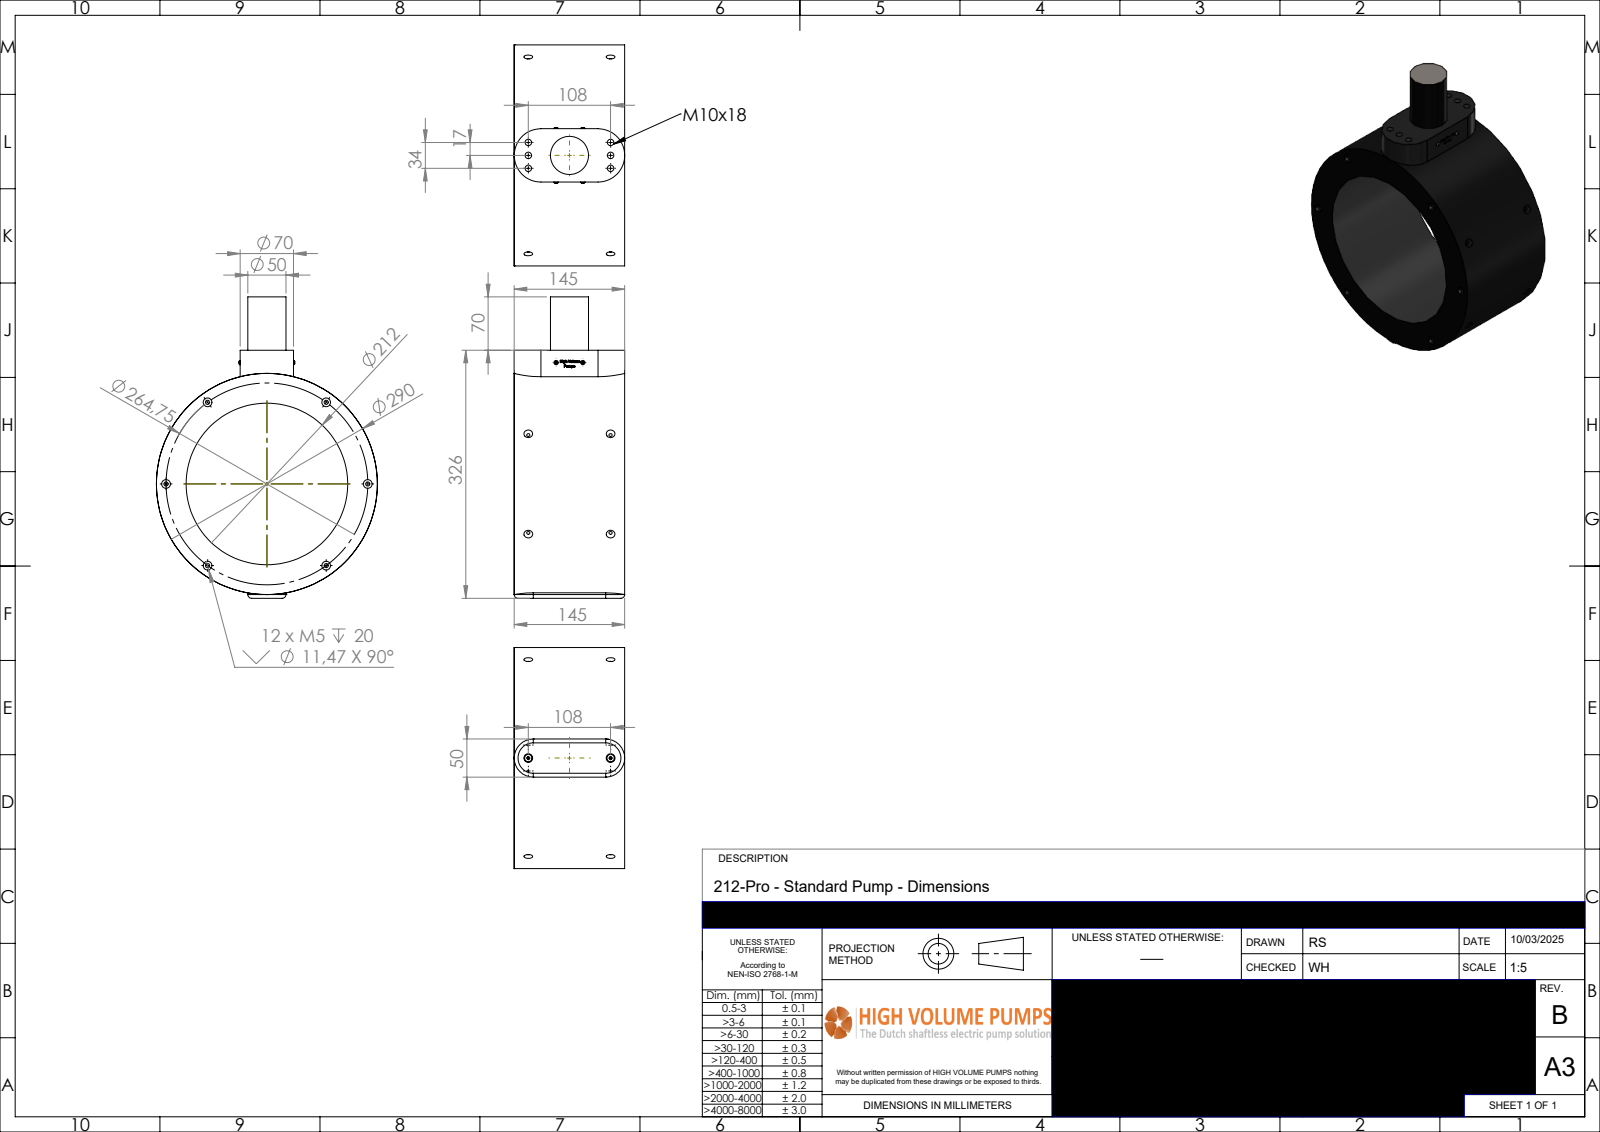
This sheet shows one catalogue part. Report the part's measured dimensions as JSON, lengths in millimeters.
{"part_name": "P-212-530-rev-B-SP", "step_written_by": "SolidWorks 2024 (AUTOMOTIVE_DESIGN)", "units": "millimeters", "bodies": {"solids": 1, "faces": 639, "planar": 337, "cylindrical": 45, "other": 257}, "overall_size": [395.45, 290, 145.06], "volume_mm3": 4906000, "surface_area_mm2": 324439, "round_holes": [[5.5, 6], [8.5, 6], [4.2, 4], [5.3, 2], [212, 1]], "round_bosses_or_shafts": [[9.64, 2], [5.7, 2], [5, 2], [290, 1], [50, 1]], "partial_cylinders_radius": [[5, 2], [25, 2], [35, 2]], "face_to_face_distances": [145.06, 325.45, 70, 395.45, 10, 60, 305, 20.45, 90.45, 50], "hole_center_spacings": [108, 17, 109.33, 120.19, 132.37, 235.9, 34, 113.23]}
